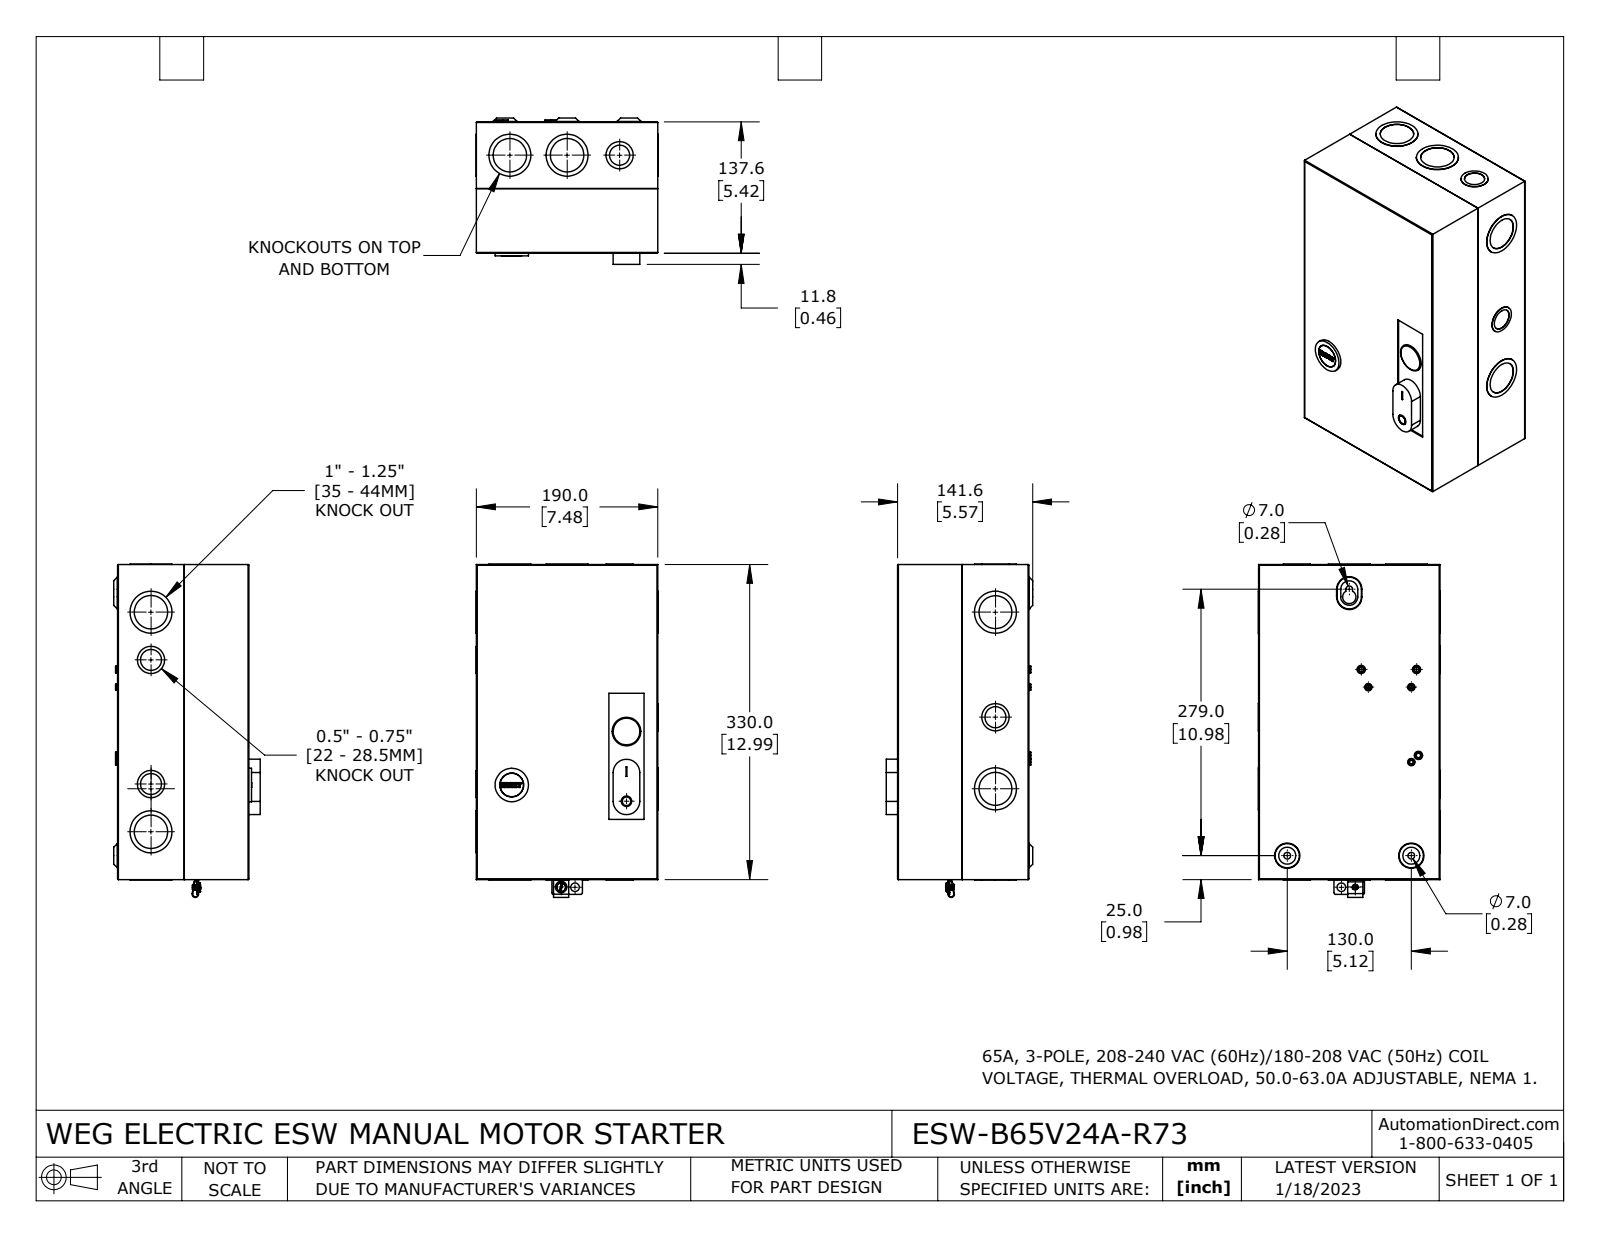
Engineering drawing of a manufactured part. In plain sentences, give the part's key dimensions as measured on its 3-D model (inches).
The part is named "ESW-B65V24A-R73". Its 3-D file was written by "SolidWorks 2021 (CONFIG_CONTROL_DESIGN)". It is 7 solids with 435 faces: 161 planar, 221 cylindrical and 53 other. Overall it measures 13.74 by 7.504 by 6.039 inches. Its volume is 24.58 cubic inches and its surface area 936.7 square inches. Round holes: 4 of diameter 1.378, 3 of diameter 0.146, 3 of diameter 0.183, 2 of diameter 0.276, 2 of diameter 0.866, 2 of diameter 0.886, 2 of diameter 1.357, 1 of diameter 0.256, 1 of diameter 0.279, 1 of diameter 0.354, 1 of diameter 0.433, 1 of diameter 0.469. Round bosses or shafts: 4 of diameter 1.732, 3 of diameter 1.122, 3 of diameter 0.278, 3 of diameter 0.24, 2 of diameter 1.734, 1 of diameter 1.378, 1 of diameter 1.193, 1 of diameter 1.148. Partial cylindrical surfaces (rounded edges, fillets, slot ends): 34 of radius 0.004, 8 of radius 0.031, 3 of radius 0.079, 3 of radius 0.138, 2 of radius 0.059, 2 of radius 0.075, 2 of radius 0.108, 2 of radius 0.122. The main face-to-face distances are 0.047, 5.37, 7.433, 5.323, 5.417, 12.945, 7.386, 7.48, 0.071, 12.898. The hole center spacings are 0.571, 1.772, 1.969, 2.283, 2.362, 5.118, 7.087, 10.972.
